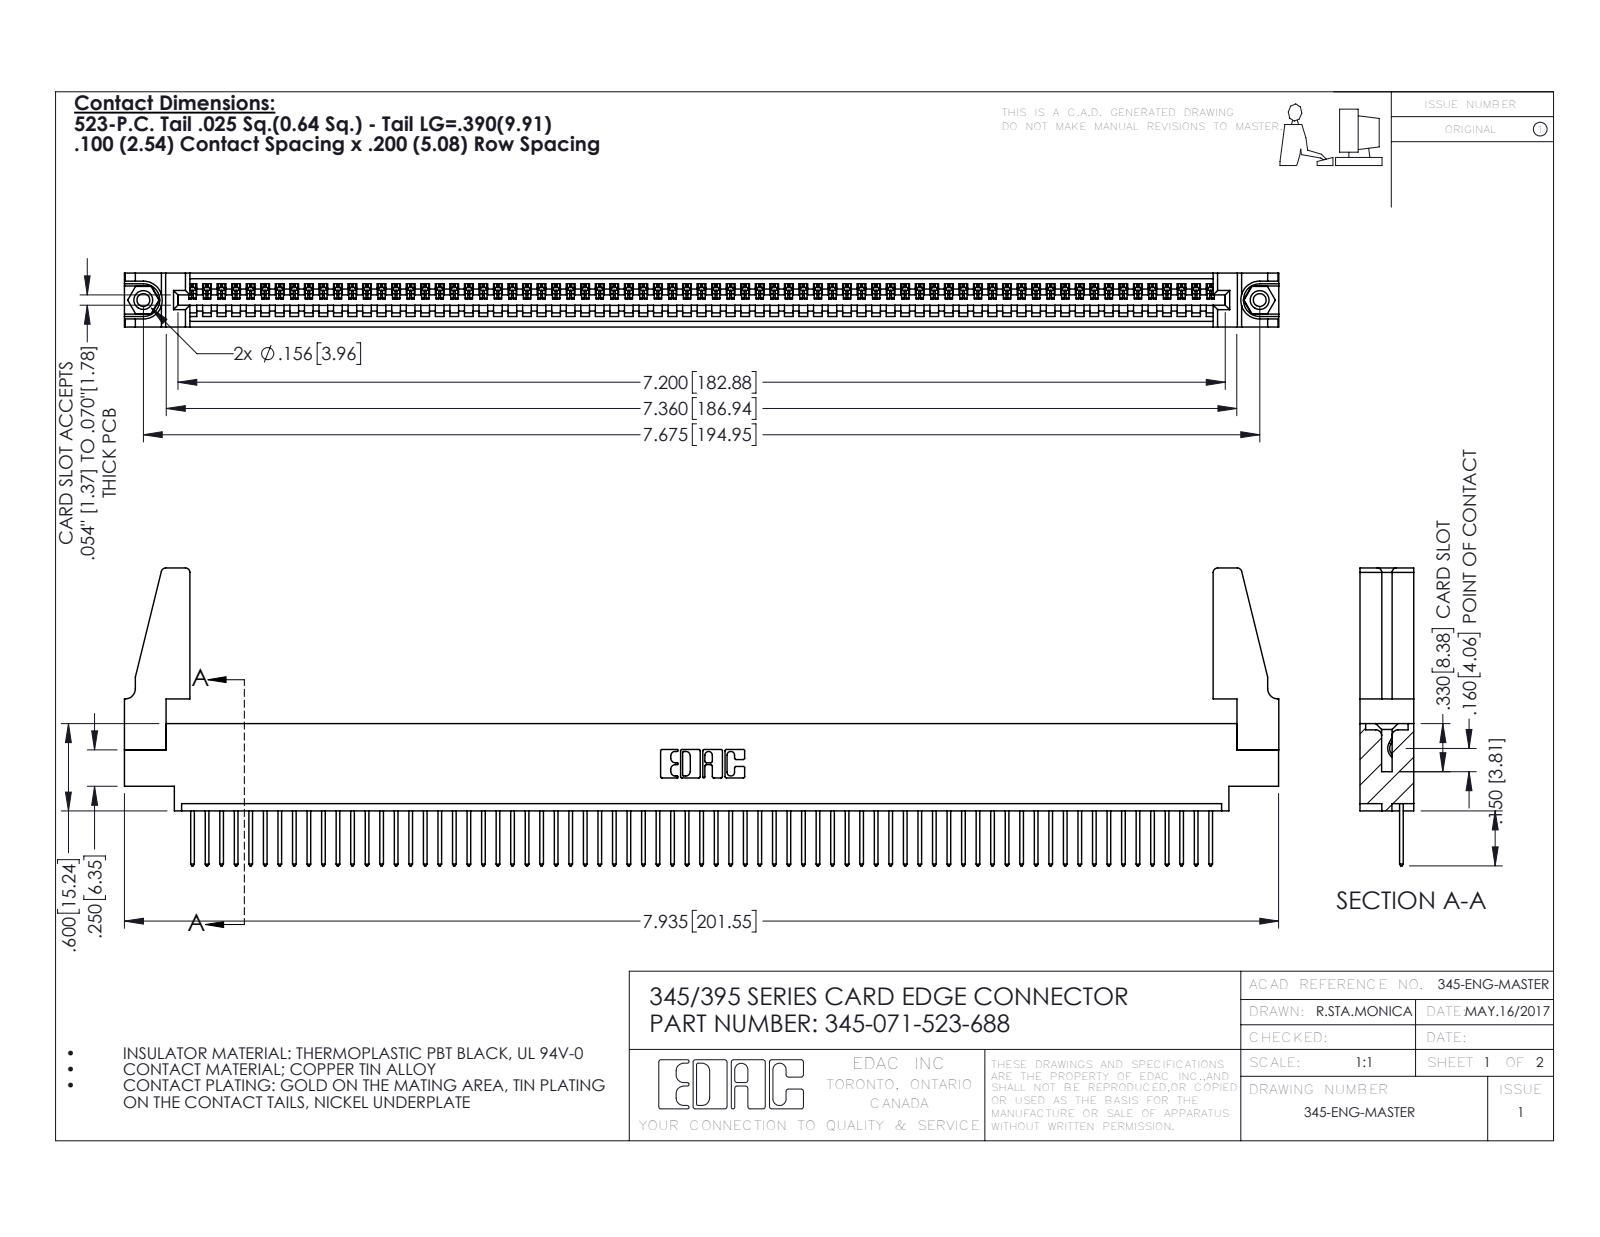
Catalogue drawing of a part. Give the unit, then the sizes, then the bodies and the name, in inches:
Units: inches
Overall size (bounding box): 7.936 × 2.047 × 0.37
Round holes (diameter × count): ⌀0.089 ×2, ⌀0.125 ×2, ⌀0.156 ×2, ⌀0.064 ×1
Round bosses / shafts (diameter × count): ⌀0.155 ×2
Partial cylindrical surfaces — rounded edges, fillets, slot ends (radius × count): R0.006 ×142, R0.01 ×142, R0.01 ×22, R0.03 ×8, R0.007 ×6, R0.031 ×6, R0.026 ×3, R0.031 ×2
Main face-to-face distances: 0.072, 0.298, 0.37, 0.098, 0.272, 0.025, 0.2, 0.225, 0.175, 0.149
Hole centre spacings: 0.27, 7.439, 7.675
Volume: 1.373 in³ · Surface area: 45.41 in²
Bodies: 76 solids, 4372 faces (2996 planar, 1360 cylindrical, 16 other)
Part name (STEP PRODUCT): 345-220-078_345-220-088; 345-250-001_345-250-001-102; 345-292-001_345-293-123; 345 Part_0.170 Offset - 0.156 Dia-TH (+1 more)
STEP written by: SolidWorks 2016 (CONFIG_CONTROL_DESIGN)
